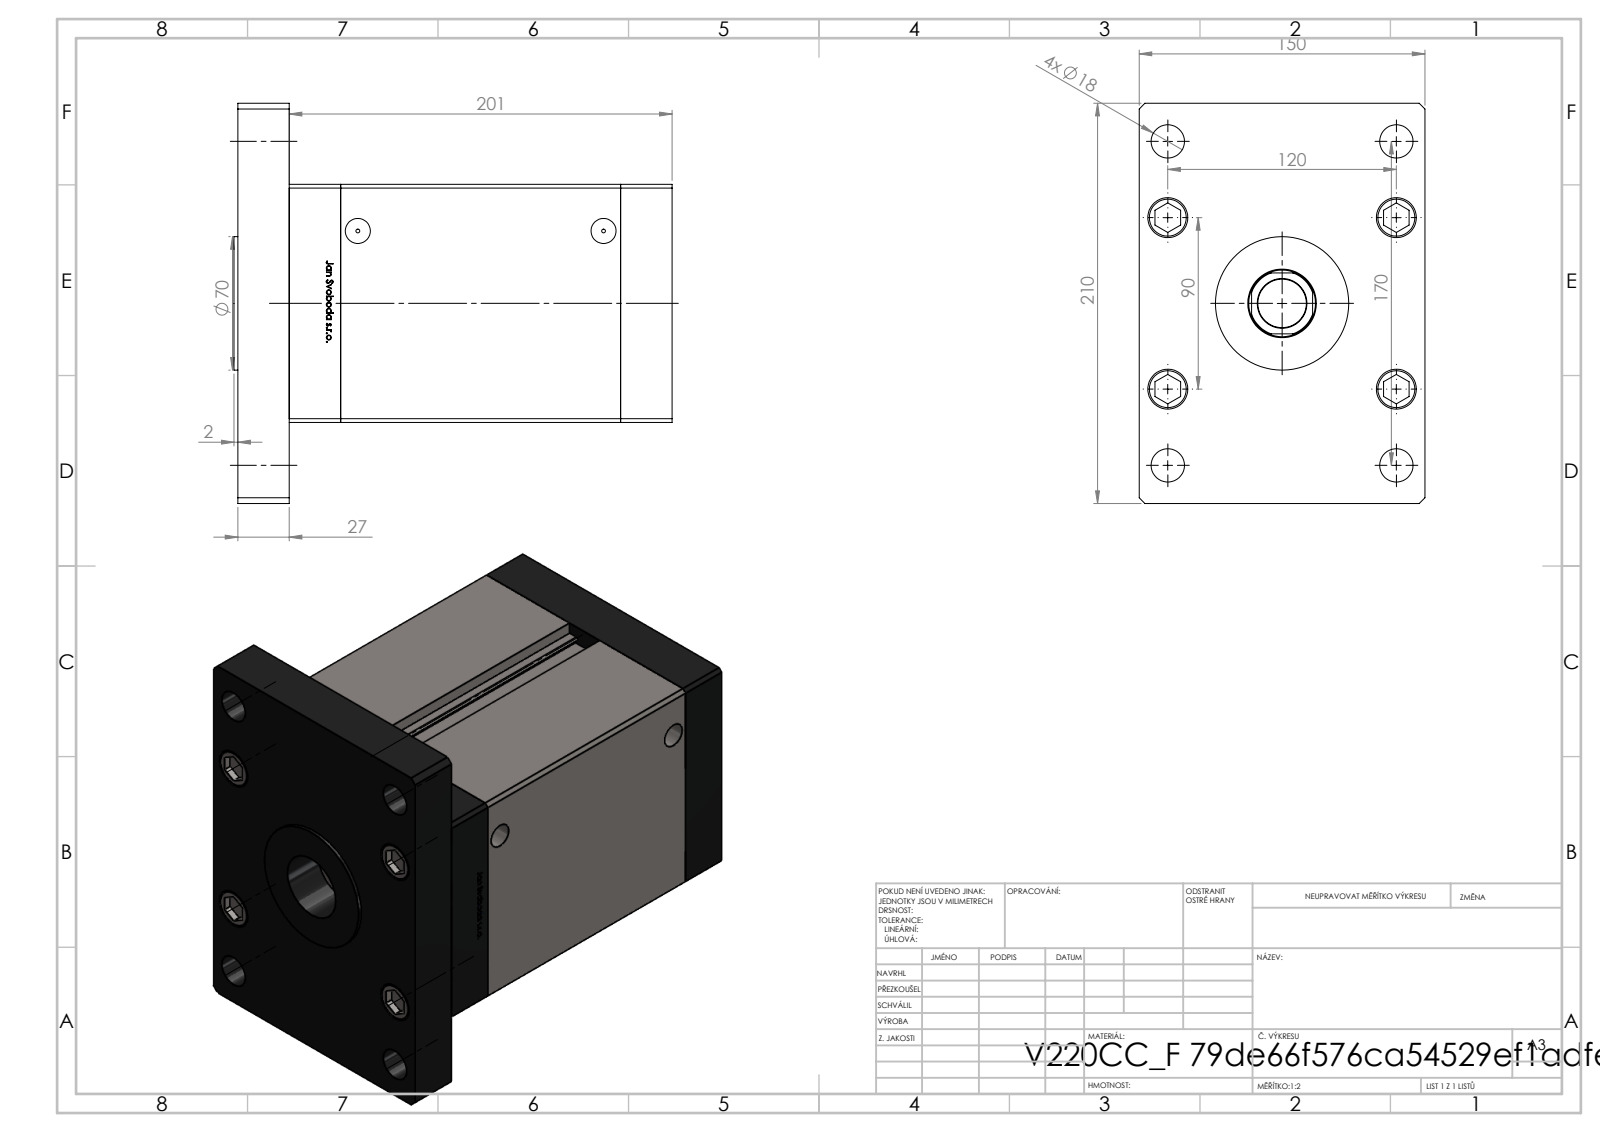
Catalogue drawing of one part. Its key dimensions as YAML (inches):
part_name: "V220C_F; V220C_VC_F; V220C_FRONT_F; V220C BACK_F (+2 more)"
step_written_by: "SolidWorks 2019 (CONFIG_CONTROL_DESIGN)"
units: inches
bodies: {solids: 19, faces: 1308, planar: 515, cylindrical: 187, other: 606}
overall_size: [9.055, 8.268, 5.906]
volume: 243.6
surface_area: 691.3
round_holes:
  - {diameter: 0.689, count: 9}
  - {diameter: 0.866, count: 5}
  - {diameter: 0.63, count: 4}
  - {diameter: 0.827, count: 4}
  - {diameter: 0.079, count: 2}
  - {diameter: 0.518, count: 2}
  - {diameter: 1.004, count: 1}
  - {diameter: 1.417, count: 1}
  - {diameter: 1.476, count: 1}
round_bosses_or_shafts:
  - {diameter: 0.315, count: 9}
  - {diameter: 0.827, count: 5}
  - {diameter: 3.15, count: 1}
  - {diameter: 2.756, count: 1}
partial_cylinders:
  - {radius: 0.037, count: 2}
  - {radius: 0.689, count: 1}
face_to_face_distances: [1.063, 6.85, 7.913, 5.906, 4.921, 5.787, 2.126, 8.976, 1.37, 0.307]
hole_center_spacings: [2.008, 1.575, 2.953, 4.096, 4.724, 4.98, 5.118, 6.965]
